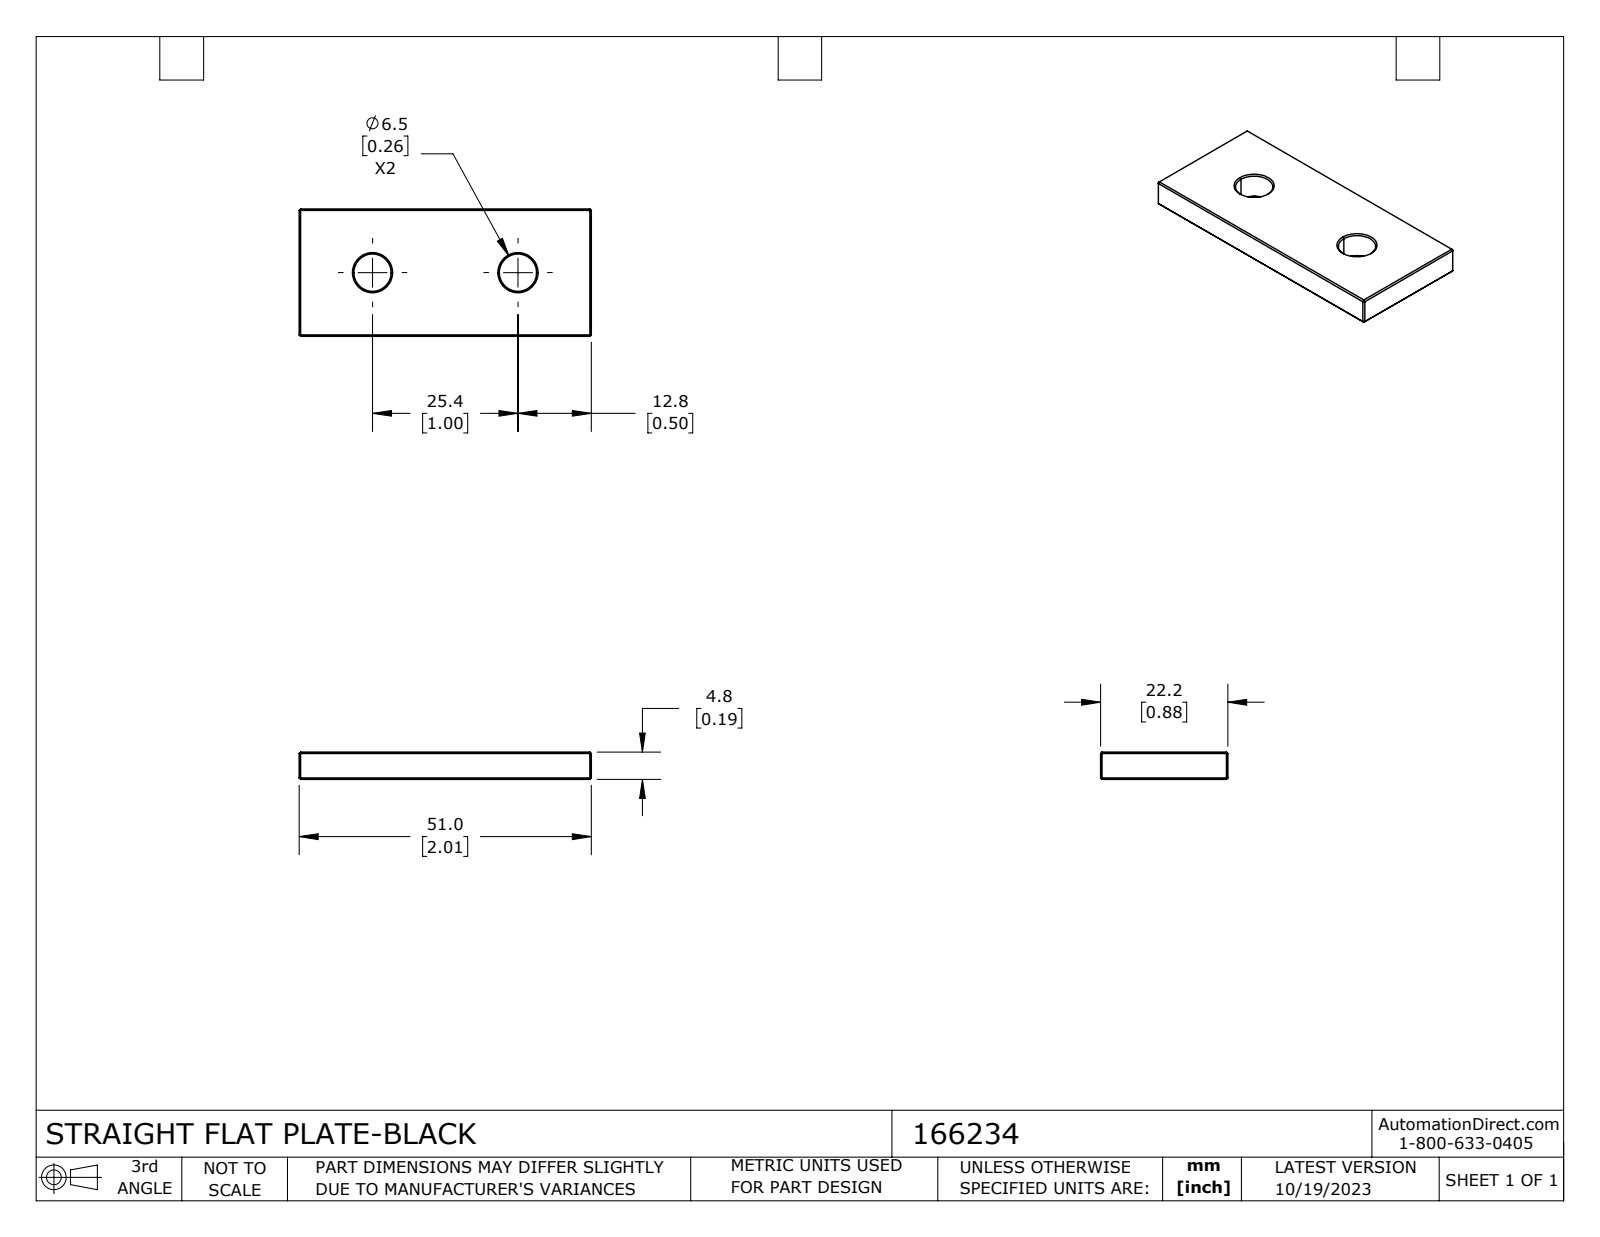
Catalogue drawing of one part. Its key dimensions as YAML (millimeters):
part_name: "166234"
step_written_by: "SolidWorks 2023 (CONFIG_CONTROL_DESIGN)"
units: millimeters
bodies: {solids: 1, faces: 38, planar: 26, cylindrical: 4, other: 8}
overall_size: [51, 22.23, 4.76]
volume: 5070
surface_area: 2969
round_holes:
  - {diameter: 6.5, count: 2}
face_to_face_distances: [4.76, 22.22, 51, 18.73, 39.07, 51.42, 44.42]
hole_center_spacings: [25.4]
